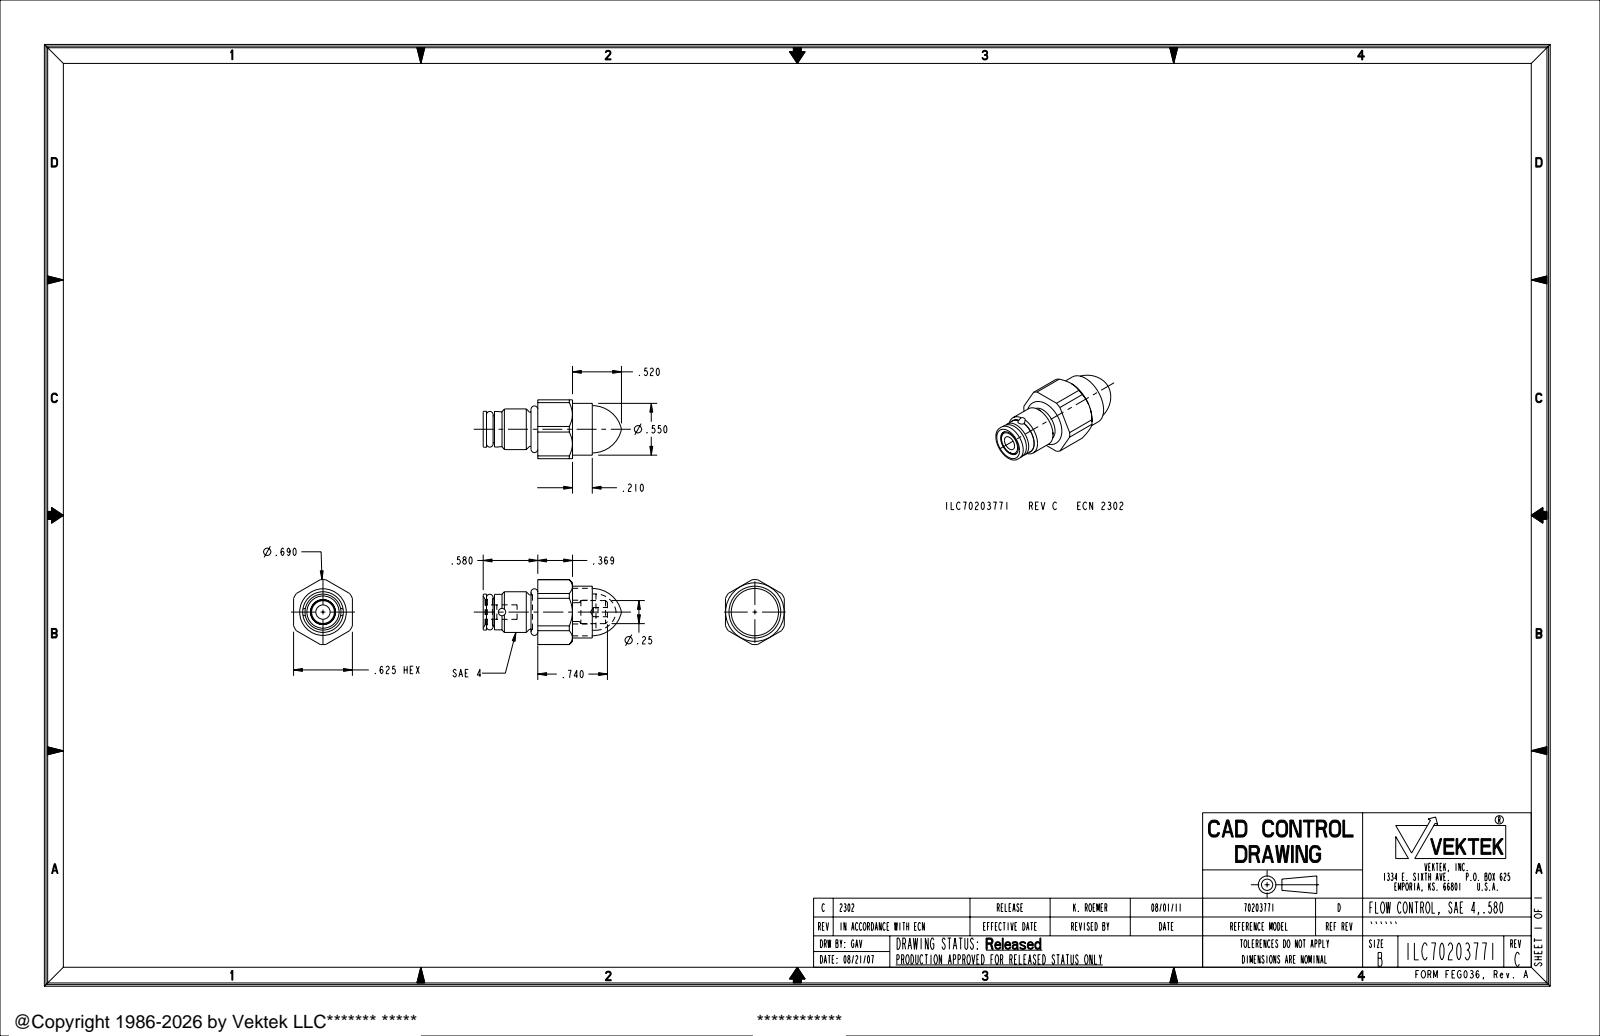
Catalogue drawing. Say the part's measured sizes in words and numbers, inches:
The part is named "ILC70203771". Its 3-D file was written by "PRO/ENGINEER BY PARAMETRIC TECHNOLOGY CORPORATION, 2007460 (AUTOMOTIVE_DESIGN_CC2)". It is 2 solids with 109 faces: 39 planar, 36 cylindrical and 34 other. Overall it measures 1.469 by 0.69 by 0.625 inches. Its volume is 0.239 cubic inches and its surface area 4.486 square inches. Round holes: 1 of diameter 0.078, 1 of diameter 0.098, 1 of diameter 0.152, 1 of diameter 0.154, 1 of diameter 0.266, 1 of diameter 0.386. Round bosses or shafts: 1 of diameter 0.55, 1 of diameter 0.432, 1 of diameter 0.382, 1 of diameter 0.377, 1 of diameter 0.364, 1 of diameter 0.262, 1 of diameter 0.245, 1 of diameter 0.2. Partial cylindrical surfaces (rounded edges, fillets, slot ends): 1 of radius 0.345. The main face-to-face distances are 0.094, 0.531, 0.625, 0.369, 0.437, 0.21, 0.579, 1.124, 0.914, 0.545.
